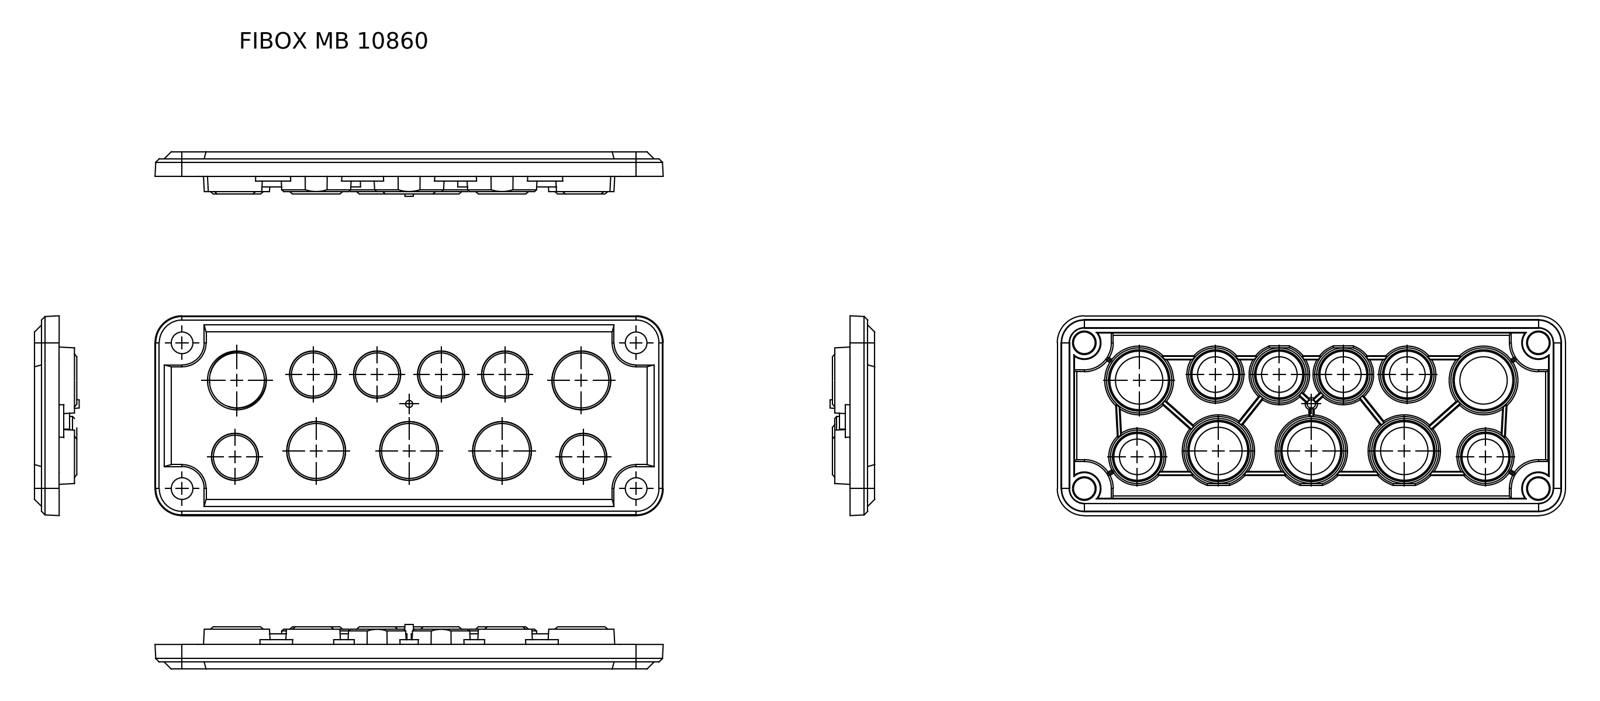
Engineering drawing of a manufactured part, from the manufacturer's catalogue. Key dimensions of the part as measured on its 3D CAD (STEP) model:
Part name (STEP PRODUCT): FIBOX MB10860
STEP written by: SolidWorks 2014 (AUTOMOTIVE_DESIGN)
Units: millimetres
Bodies: 1 solid, 364 faces (187 planar, 28 cylindrical, 149 other)
Overall size (bounding box): 216 × 85 × 19
Volume: 93 315 mm³ · Surface area: 78 014 mm²
Round holes (diameter × count): ⌀18.38 ×6, ⌀23.38 ×4, ⌀23.3 ×1, ⌀25 ×1
Partial cylindrical surfaces — rounded edges, fillets, slot ends (radius × count): R1.6 ×4
Main face-to-face distances: 2.5, 16, 13.5, 7.5, 2, 18, 15.5, 5.5, 15, 10.5
Hole centre spacings: 27.2, 32.5, 32.51, 32.53, 34.59, 35.23, 39.5, 41.56
